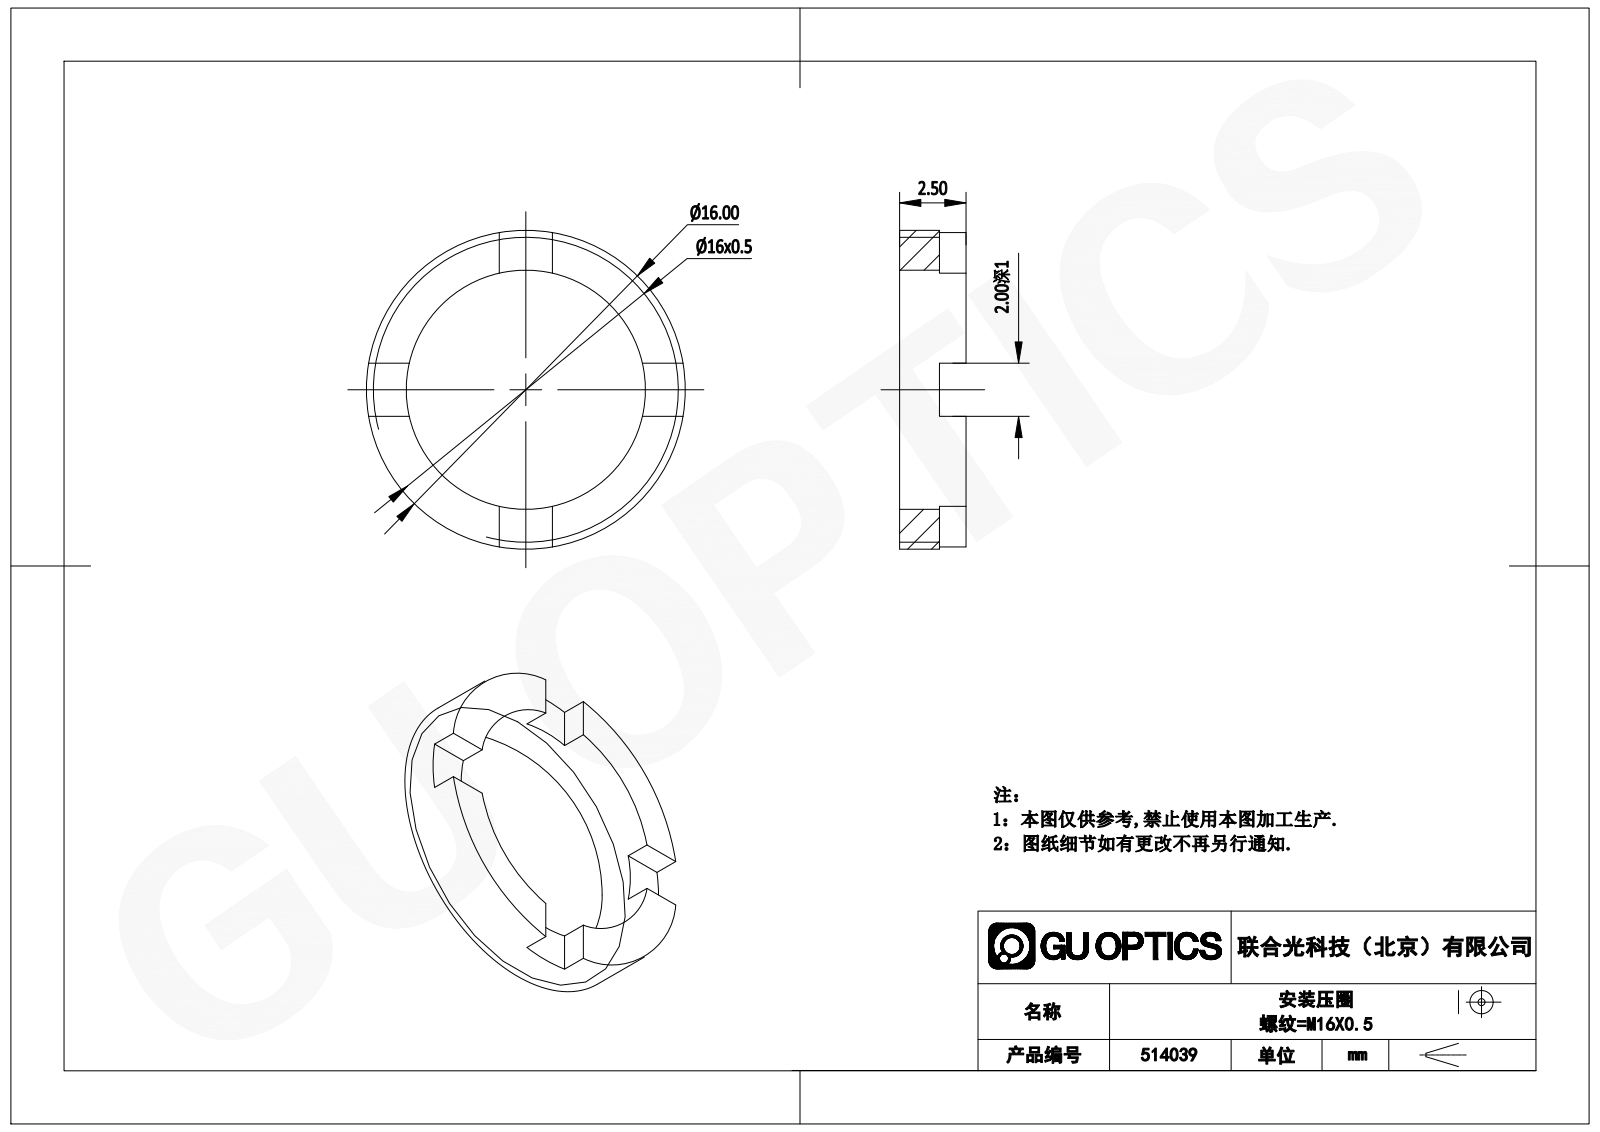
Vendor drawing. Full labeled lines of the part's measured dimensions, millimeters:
Part name (STEP PRODUCT): 514039
STEP written by: SolidWorks 2020 (CONFIG_CONTROL_DESIGN)
Units: millimetres
Bodies: 1 solid, 21 faces (17 planar, 4 cylindrical, 0 other)
Overall size (bounding box): 16 × 16 × 2.5
Volume: 159 mm³ · Surface area: 360 mm²
Round holes (diameter × count): ⌀13 ×1
Round bosses / shafts (diameter × count): ⌀16 ×1
Main face-to-face distances: 2.5, 1.5, 1, 2
